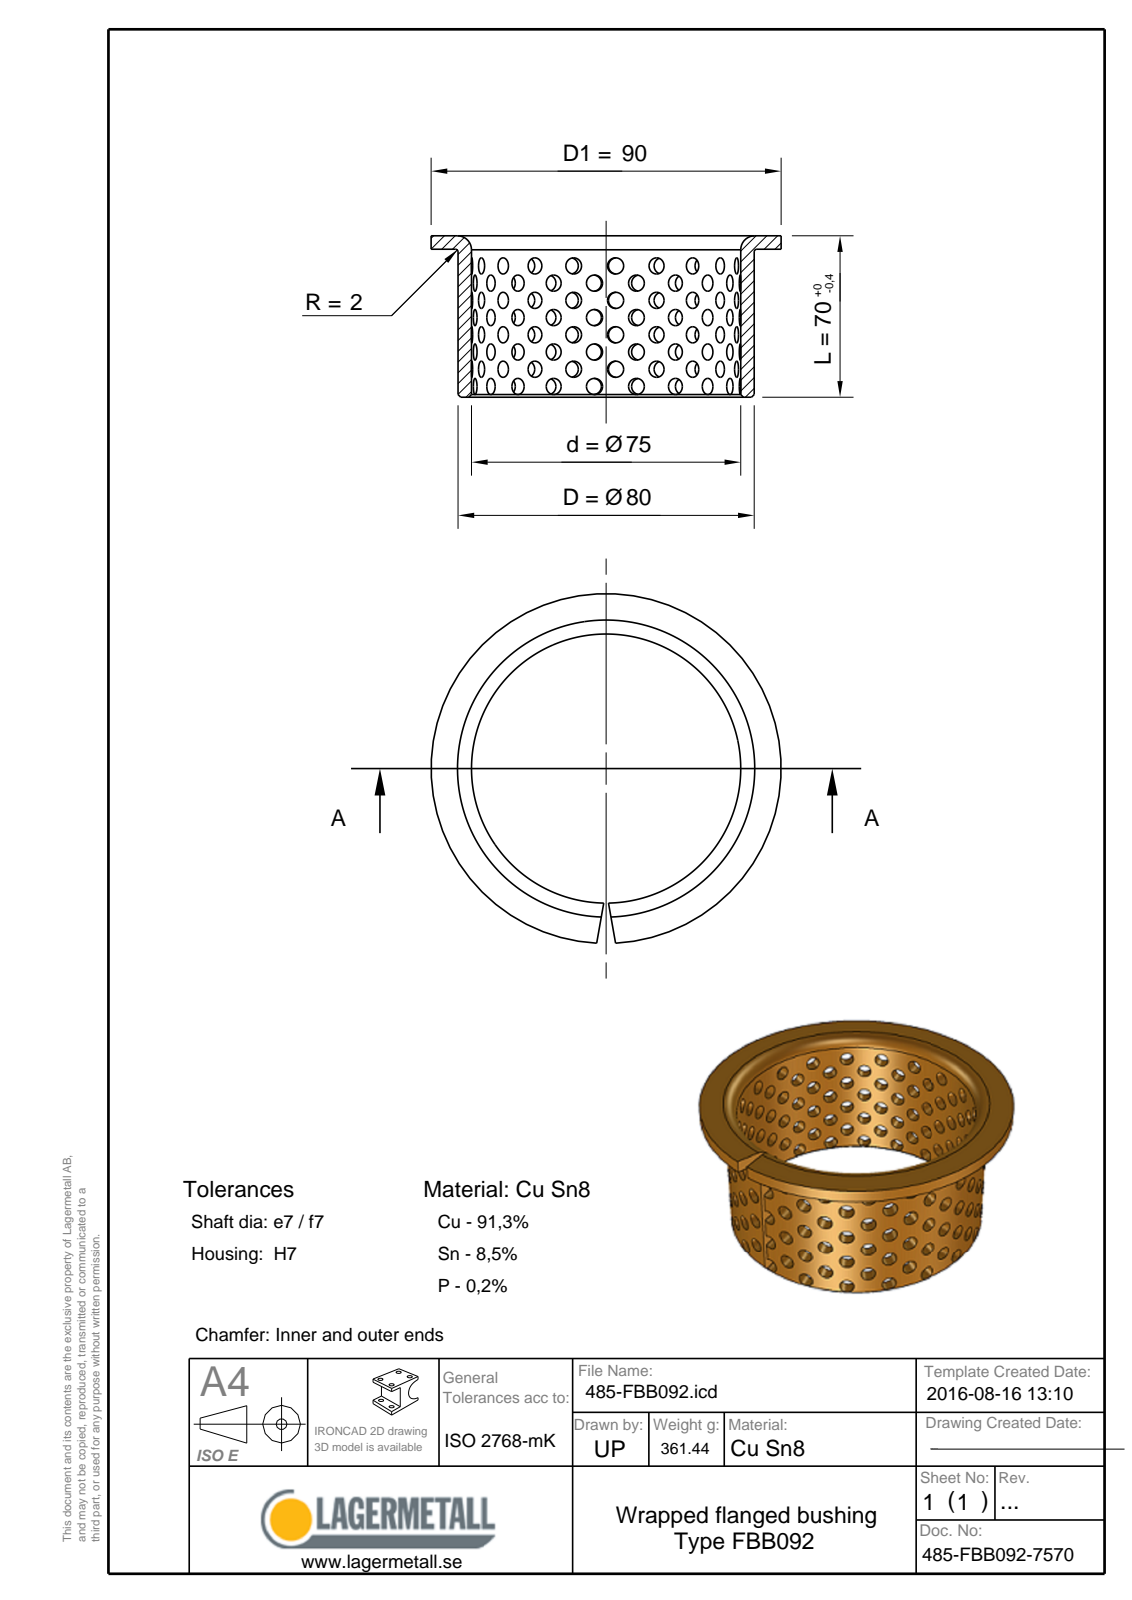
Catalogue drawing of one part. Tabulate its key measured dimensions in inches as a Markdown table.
| quantity | value |
| --- | --- |
| part name | 485-FBB092-7570 |
| STEP written by | Spatial InterOp 3D (CONFIG_CONTROL_DESIGN) |
| units | inches |
| bodies | 1 solid, 12 faces (5 planar, 3 cylindrical, 4 other) |
| overall size | 3.543 × 3.542 × 2.756 |
| volume | 2.723 in³ |
| surface area | 57.81 in² |
| round holes (diameter × count) | 2.953 × 1 |
| round bosses / shafts (diameter × count) | 3.543 × 1, 3.15 × 1 |
| main face-to-face distances | 0.098, 2.657, 2.756 |
